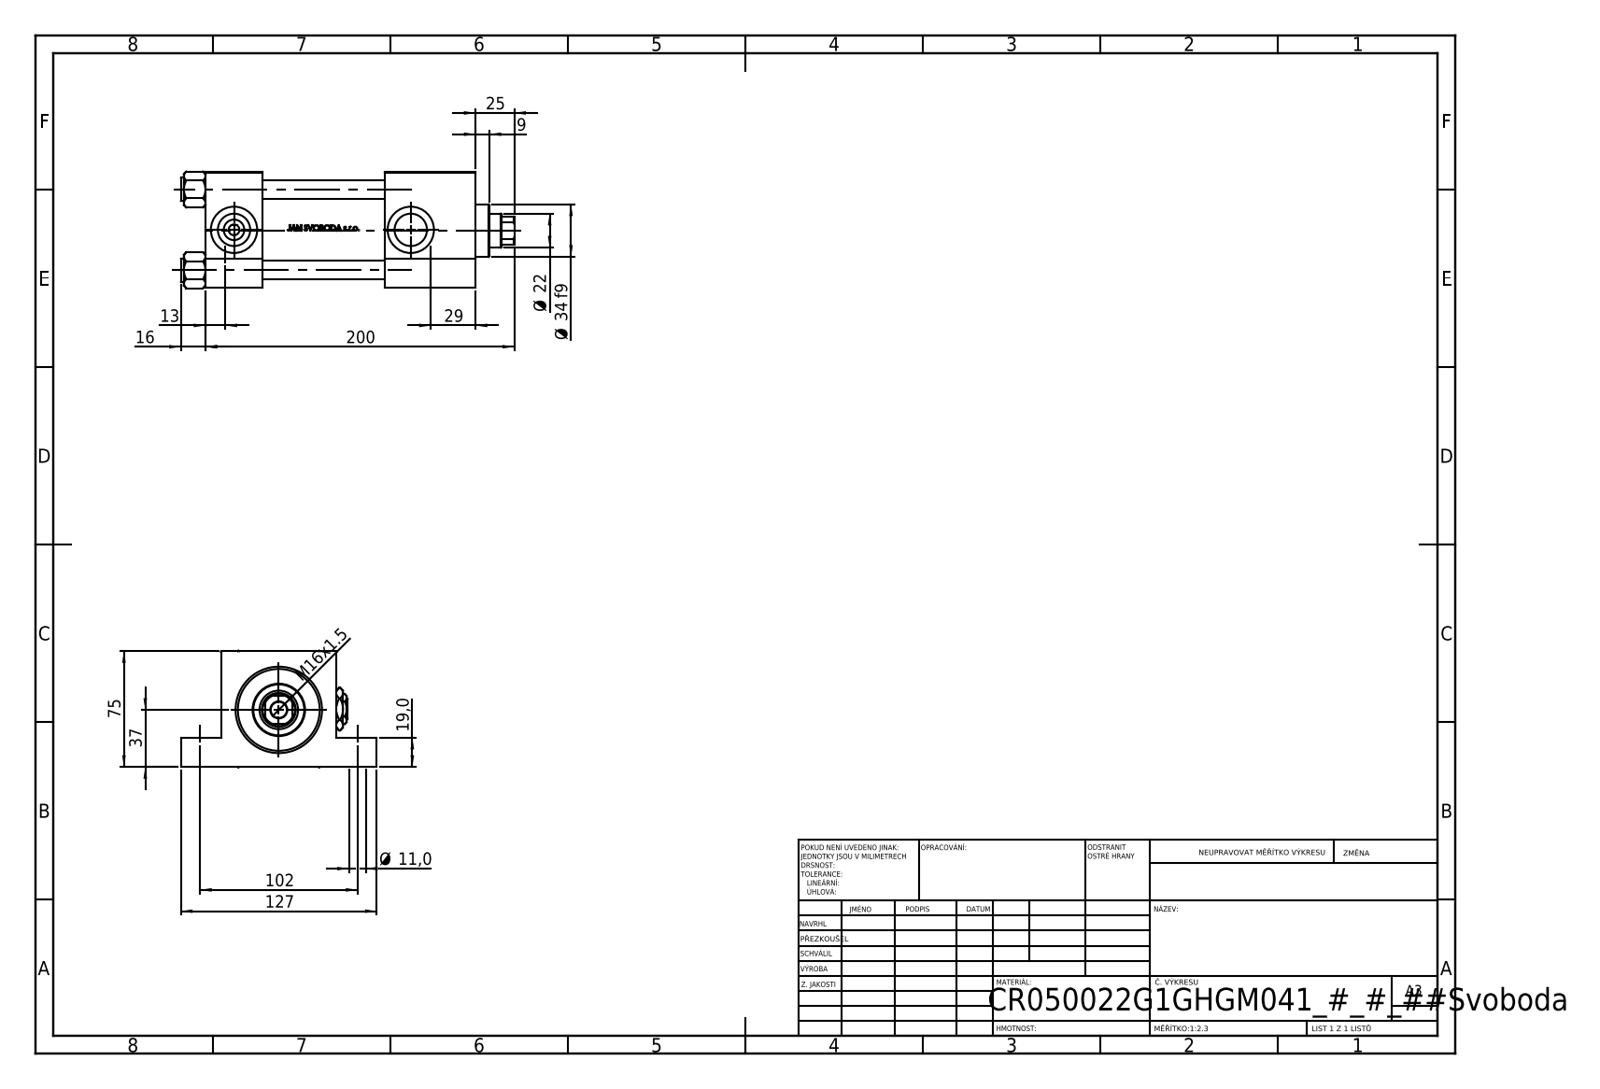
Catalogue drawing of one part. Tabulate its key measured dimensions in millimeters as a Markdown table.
| quantity | value |
| --- | --- |
| part name | V215CR_VCP_G; V215_VC_A; V215CR_G_TYCINKA; Zatka_pro_OIL_PORT (+2 more) |
| STEP written by | SolidWorks 2019 (CONFIG_CONTROL_DESIGN) |
| units | millimeters |
| bodies | 12 solids, 1134 faces (454 planar, 128 cylindrical, 552 other) |
| overall size | 216 × 127 × 75.54 |
| volume | 780 376 mm³ |
| surface area | 172 915 mm² |
| round holes (diameter × count) | 11 × 4, 12 × 4, 7 × 2, 20.96 × 2, 30 × 2, 10.5 × 1, 22 × 1, 25 × 1, 41 × 1, 50 × 1, 53 × 1 |
| round bosses / shafts (diameter × count) | 15 × 4, 56 × 1, 34 × 1 |
| partial cylindrical surfaces (radius × count) | 10.5 × 1 |
| main face-to-face distances | 75, 37, 175, 138, 19, 56, 79, 116, 59, 26 |
| hole center spacings | 52.3, 36.63, 37.34, 73.96, 102, 133, 167.61, 114.5 |
